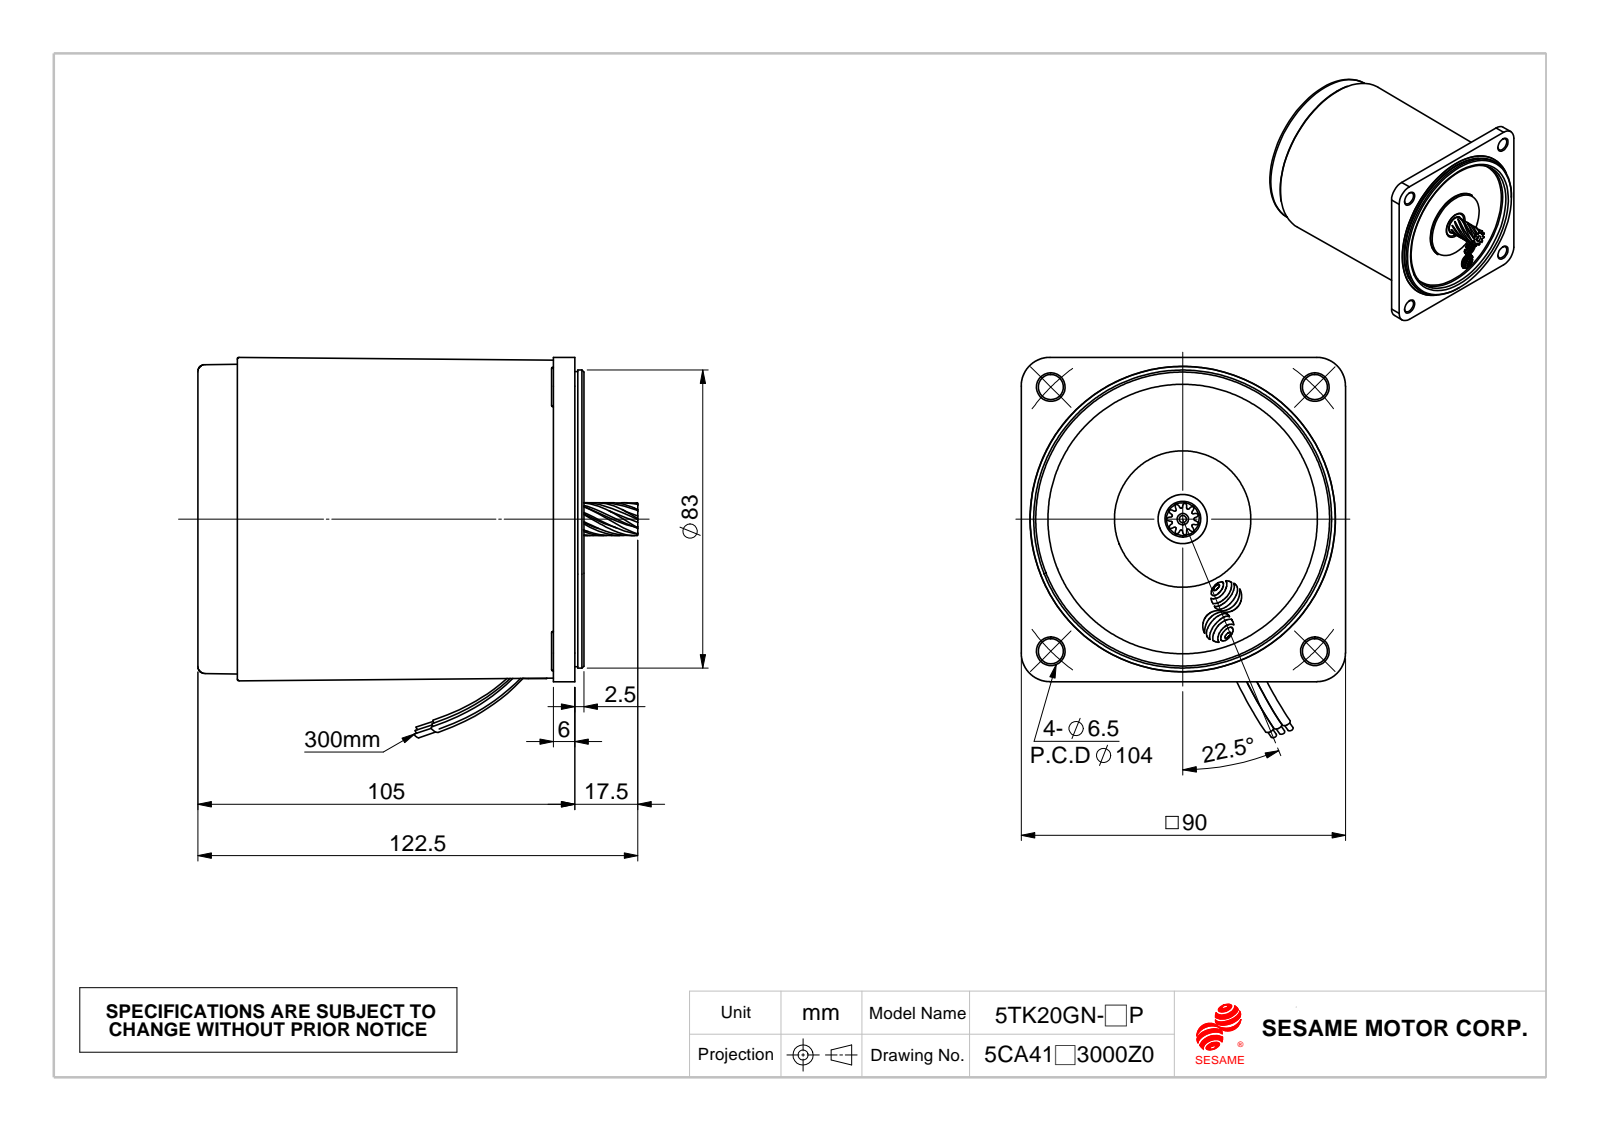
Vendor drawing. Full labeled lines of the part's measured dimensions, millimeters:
Part name (STEP PRODUCT): M540; 線扣; 40GN
STEP written by: SolidWorks 2010 (CONFIG_CONTROL_DESIGN)
Units: millimetres
Bodies: 7 solids, 402 faces (73 planar, 203 cylindrical, 126 other)
Overall size (bounding box): 122.5 × 105.88 × 90.3
Volume: 662 518 mm³ · Surface area: 65 518 mm²
Round holes (diameter × count): ⌀7 ×4, ⌀2 ×1, ⌀2.5 ×1, ⌀7.2 ×1, ⌀9.5 ×1, ⌀13.7 ×1, ⌀26 ×1, ⌀58.1 ×1, ⌀75 ×1, ⌀84.4 ×1, ⌀85 ×1
Round bosses / shafts (diameter × count): ⌀84.22 ×1, ⌀84.15 ×1, ⌀83 ×1, ⌀82.2 ×1, ⌀38 ×1, ⌀10 ×1, ⌀9.3 ×1, ⌀9.17 ×1
Partial cylindrical surfaces — rounded edges, fillets, slot ends (radius × count): R0.25 ×8, R0.78 ×8, R1.5 ×8, R1.66 ×8, R2.92 ×8, R0.2 ×4, R0.58 ×4, R2.58 ×4
Main face-to-face distances: 1, 102.5, 0.9, 103.5, 2.5, 101.5, 102.4, 103.4, 1.5, 104
Hole centre spacings: 52, 73.54, 104
